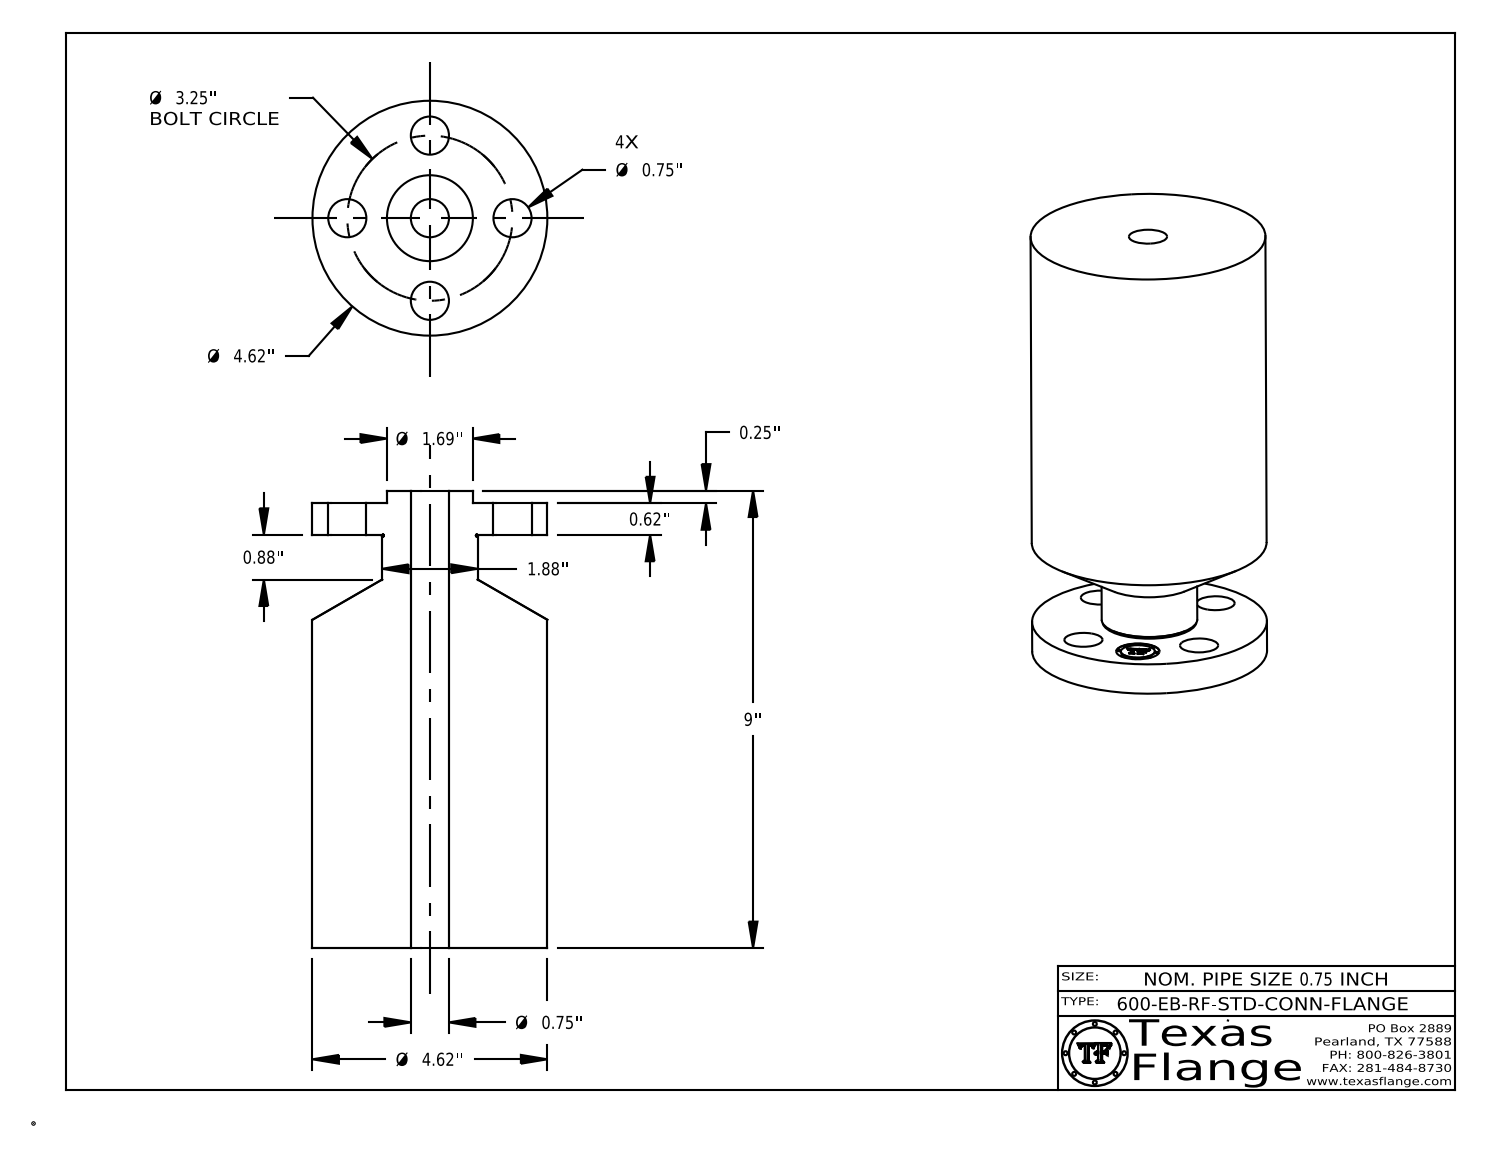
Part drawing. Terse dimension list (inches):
name: 0.75-600-EB-RF-STD-CONN-FLANGE
written by: CATIA V5 STEP AP214 (AUTOMOTIVE_DESIGN)
unit: in
bodies: 1 solid, 413 faces (369 planar, 38 cylindrical, 6 other)
size: 9 × 4.62 × 4.62
volume: 123.5 in³; area: 195.8 in²
holes: 5× ⌀0.75, 1× ⌀0.85
bosses: 8× ⌀0.051, 1× ⌀4.62, 1× ⌀1.88, 1× ⌀1.69, 1× ⌀0.67
face distances: 8.75, 0.62, 8.13, 0.25, 0.87, 9, 0.865, 0.615, 8.135, 0.254
hole spacings: 1.625, 2.298, 1.244, 3.003, 3.25
